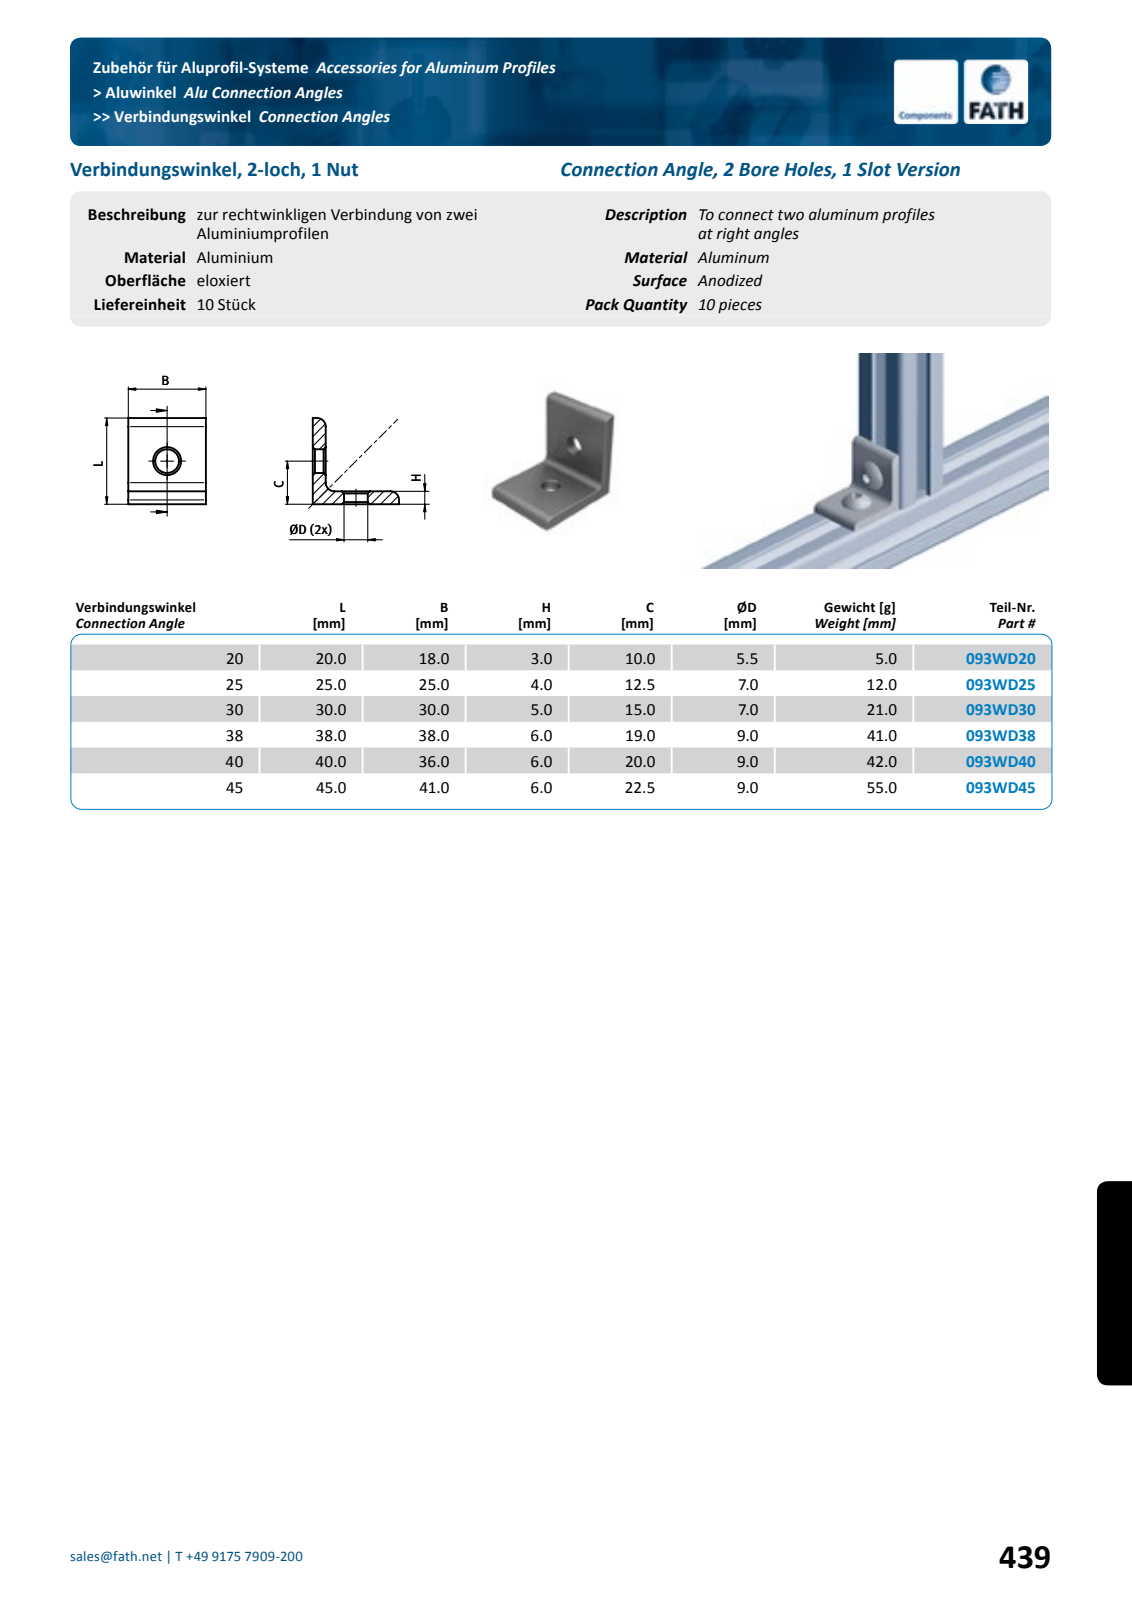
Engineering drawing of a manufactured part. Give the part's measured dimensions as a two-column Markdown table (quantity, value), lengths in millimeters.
| quantity | value |
| --- | --- |
| part name | fath_093wd40 |
| STEP written by | Spatial InterOp 3D (automotive_design) |
| units | millimeters |
| bodies | 1 solid, 23 faces (8 planar, 7 cylindrical, 8 other) |
| overall size | 40 × 40 × 36 |
| volume | 15 082 mm³ |
| surface area | 6 509 mm² |
| round holes (diameter × count) | 9 × 2 |
| partial cylindrical surfaces (radius × count) | 4 × 3 |
| main face-to-face distances | 6, 36, 40, 34 |
